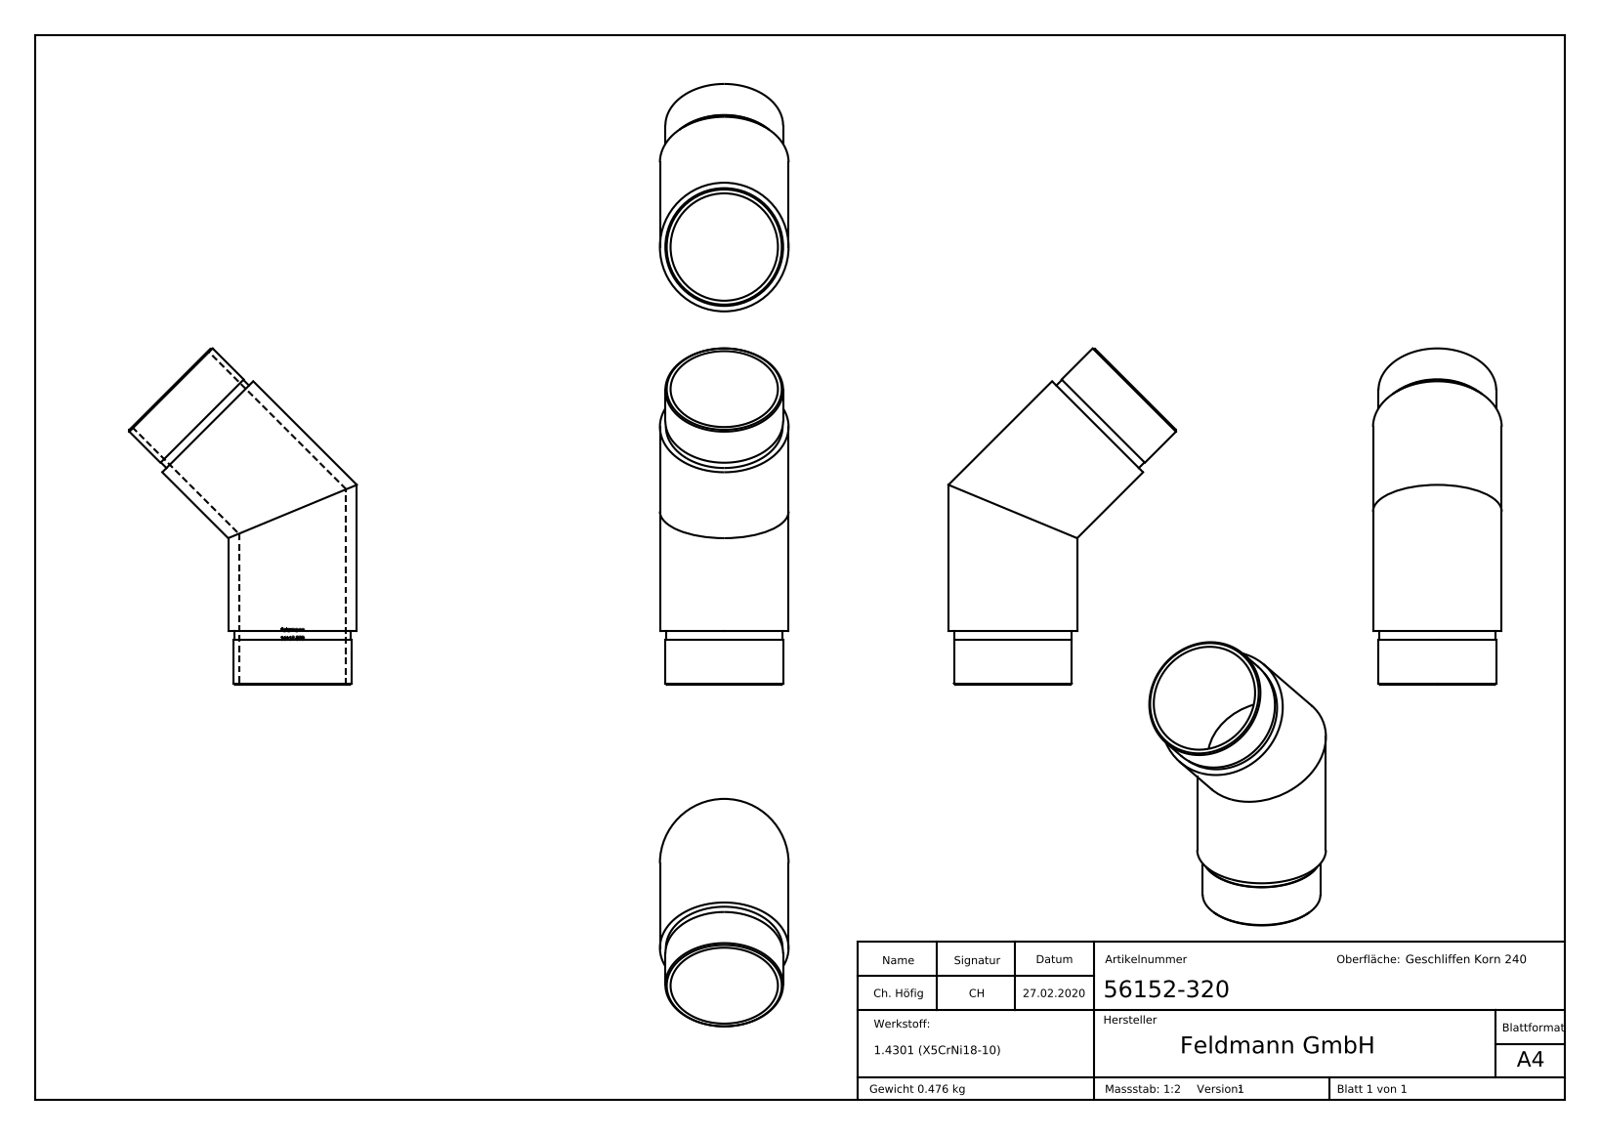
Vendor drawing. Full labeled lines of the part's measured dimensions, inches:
Part name (STEP PRODUCT): 56152-320
STEP written by: SolidWorks 2015 (CONFIG_CONTROL_DESIGN)
Units: inches
Bodies: 1 solid, 240 faces (100 planar, 30 cylindrical, 110 other)
Overall size (bounding box): 4.97 × 3.361 × 1.902
Volume: 3.677 in³ · Surface area: 57.06 in²
Round holes (diameter × count): ⌀1.587 ×2
Round bosses / shafts (diameter × count): ⌀1.902 ×2, ⌀1.74 ×2, ⌀1.724 ×2
Partial cylindrical surfaces — rounded edges, fillets, slot ends (radius × count): R0.797 ×1
Main face-to-face distances: 0.787, 0.669, 0.118, 0.015, 0.044, 0.05, 0.117, 0.052, 0.167, 0.126
